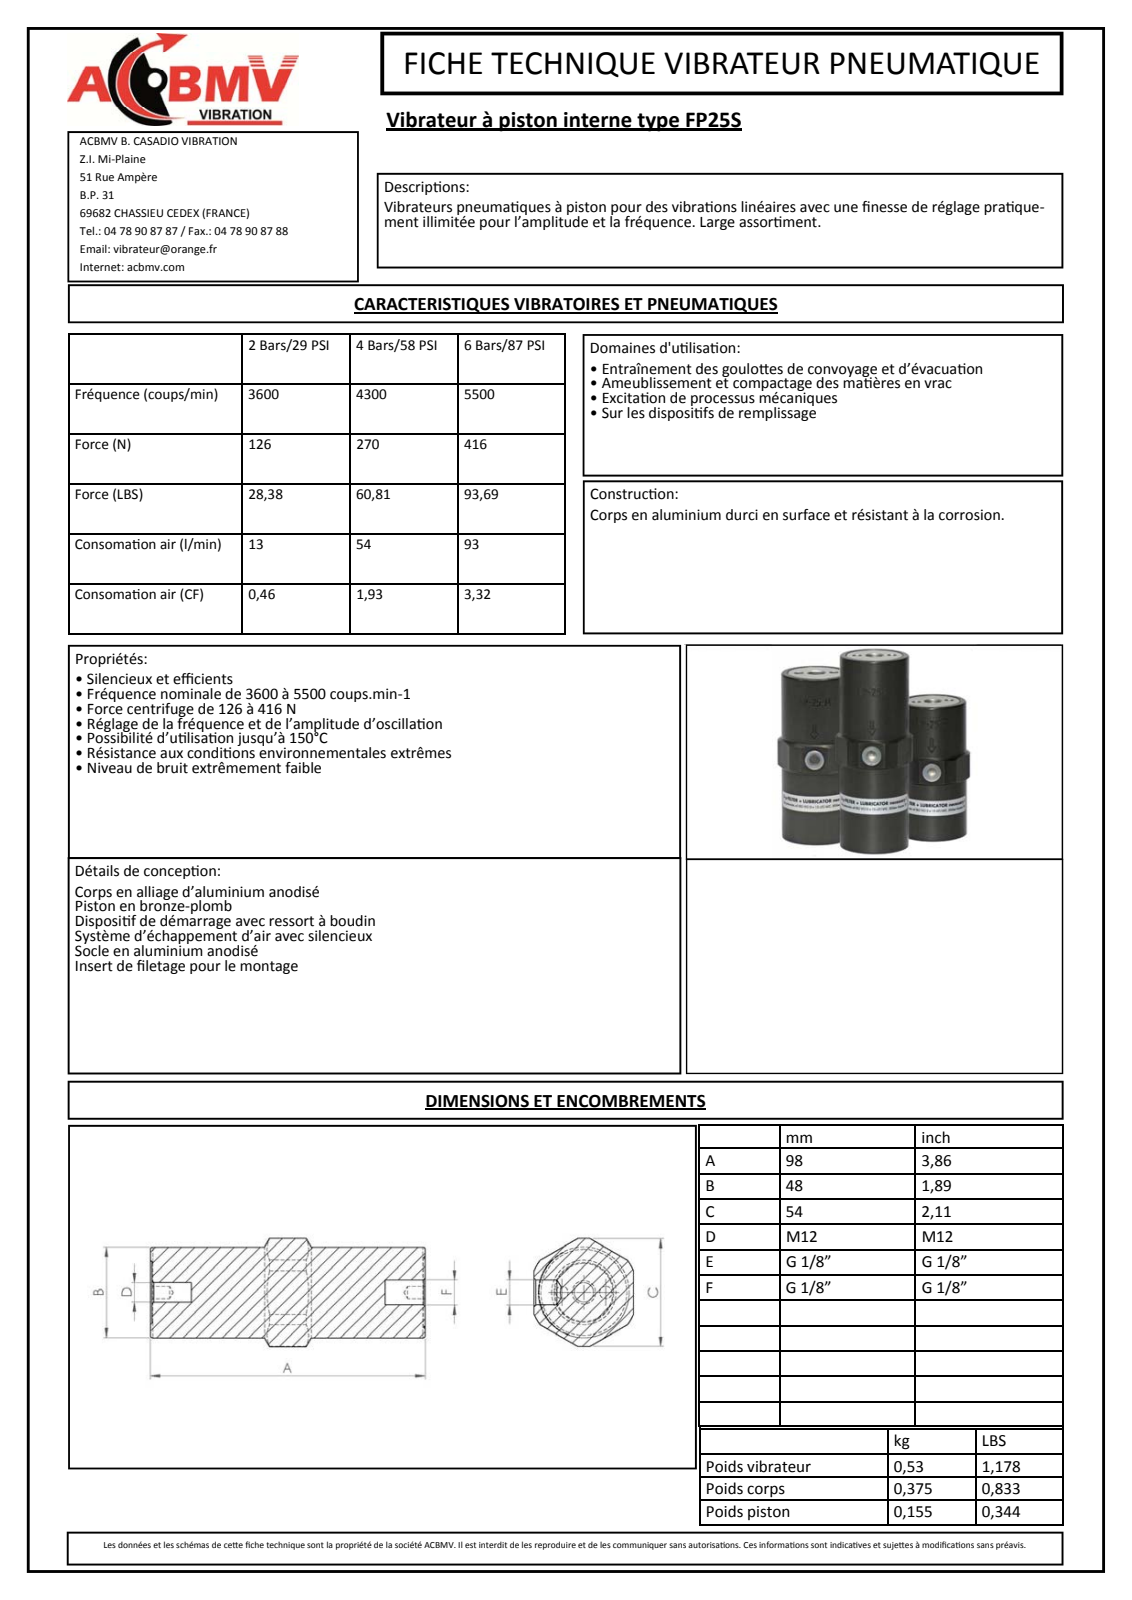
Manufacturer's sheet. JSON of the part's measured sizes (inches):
{"part_name": "9025-10-M", "step_written_by": "Autodesk Inventor 2011 (CONFIG_CONTROL_DESIGN)", "units": "inches", "bodies": {"solids": 1, "faces": 454, "planar": 180, "cylindrical": 57, "other": 217}, "overall_size": [3.858, 2.106, 1.969], "volume_in3": 10.86, "surface_area_in2": 32.53, "round_holes": [[0.244, 4], [0.098, 1], [0.337, 1], [0.398, 1], [0.451, 1]], "round_bosses_or_shafts": [[1.89, 1]], "partial_cylinders_radius": [[0.571, 1], [0.937, 1], [0.948, 1], [0.949, 1], [1.053, 1]], "face_to_face_distances": [1.969, 3.858, 0.02, 3.839, 3.319, 3.299, 0.539, 3.11, 0.748, 0.728], "hole_center_spacings": [0.039, 0.433, 0.472, 0.906, 0.866, 0.945]}
